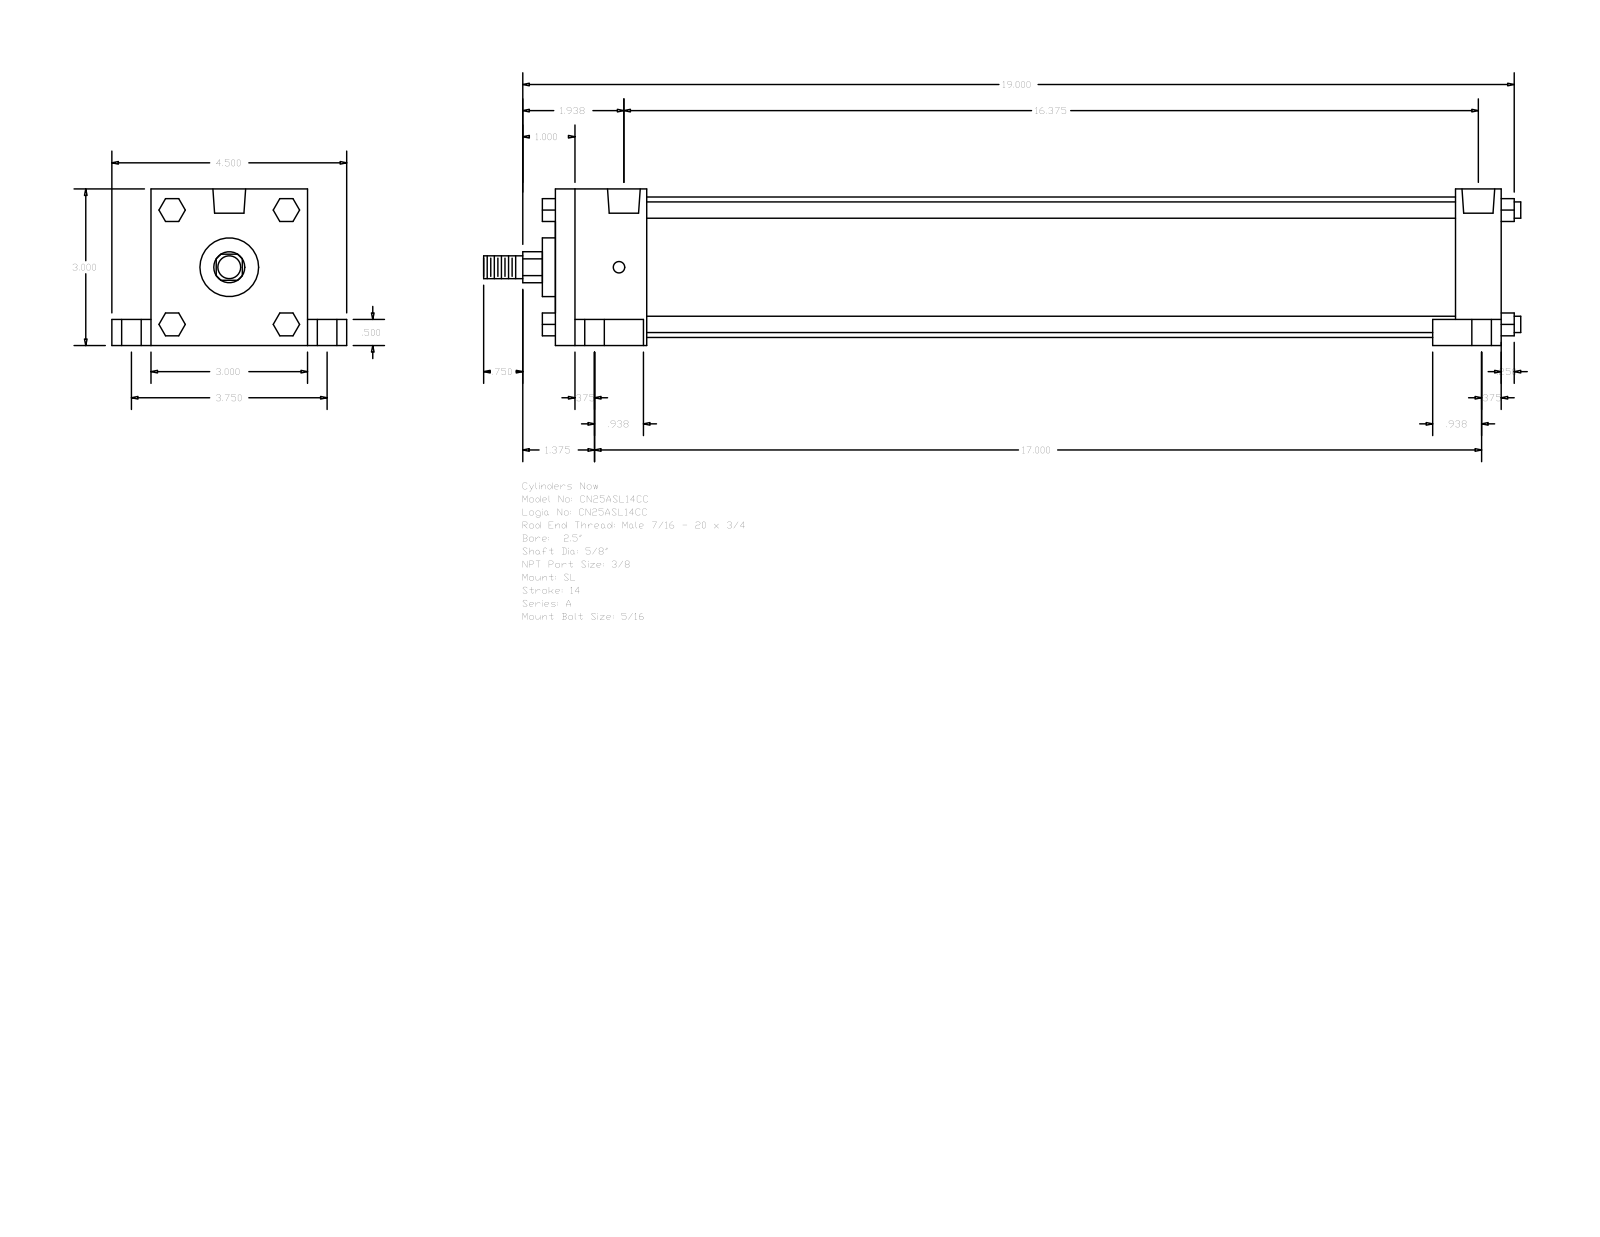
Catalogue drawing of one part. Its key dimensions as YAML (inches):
part_name: "A_SL__0250_0.625"
step_written_by: "GSSL Pune (CONFIG_CONTROL_DESIGN)"
units: inches
bodies: {solids: 0, faces: 148, planar: 112, cylindrical: 36, other: 0}
overall_size: [19.875, 4.5, 3]
round_holes:
  - {diameter: 0.219, count: 4}
  - {diameter: 0.375, count: 4}
  - {diameter: 0.625, count: 4}
  - {diameter: 0.627, count: 2}
round_bosses_or_shafts:
  - {diameter: 0.313, count: 4}
  - {diameter: 2.69, count: 1}
  - {diameter: 1.125, count: 1}
  - {diameter: 0.625, count: 1}
  - {diameter: 0.437, count: 1}
partial_cylinders:
  - {radius: 0.297, count: 1}
face_to_face_distances: [3, 18.125, 1.75, 16.375, 17.25, 15.5, 0.875, 2.5, 0.5, 0.75]
hole_center_spacings: [0.094, 1.875, 1.876, 1.933, 1.957, 3.75, 16.469, 16.544]
